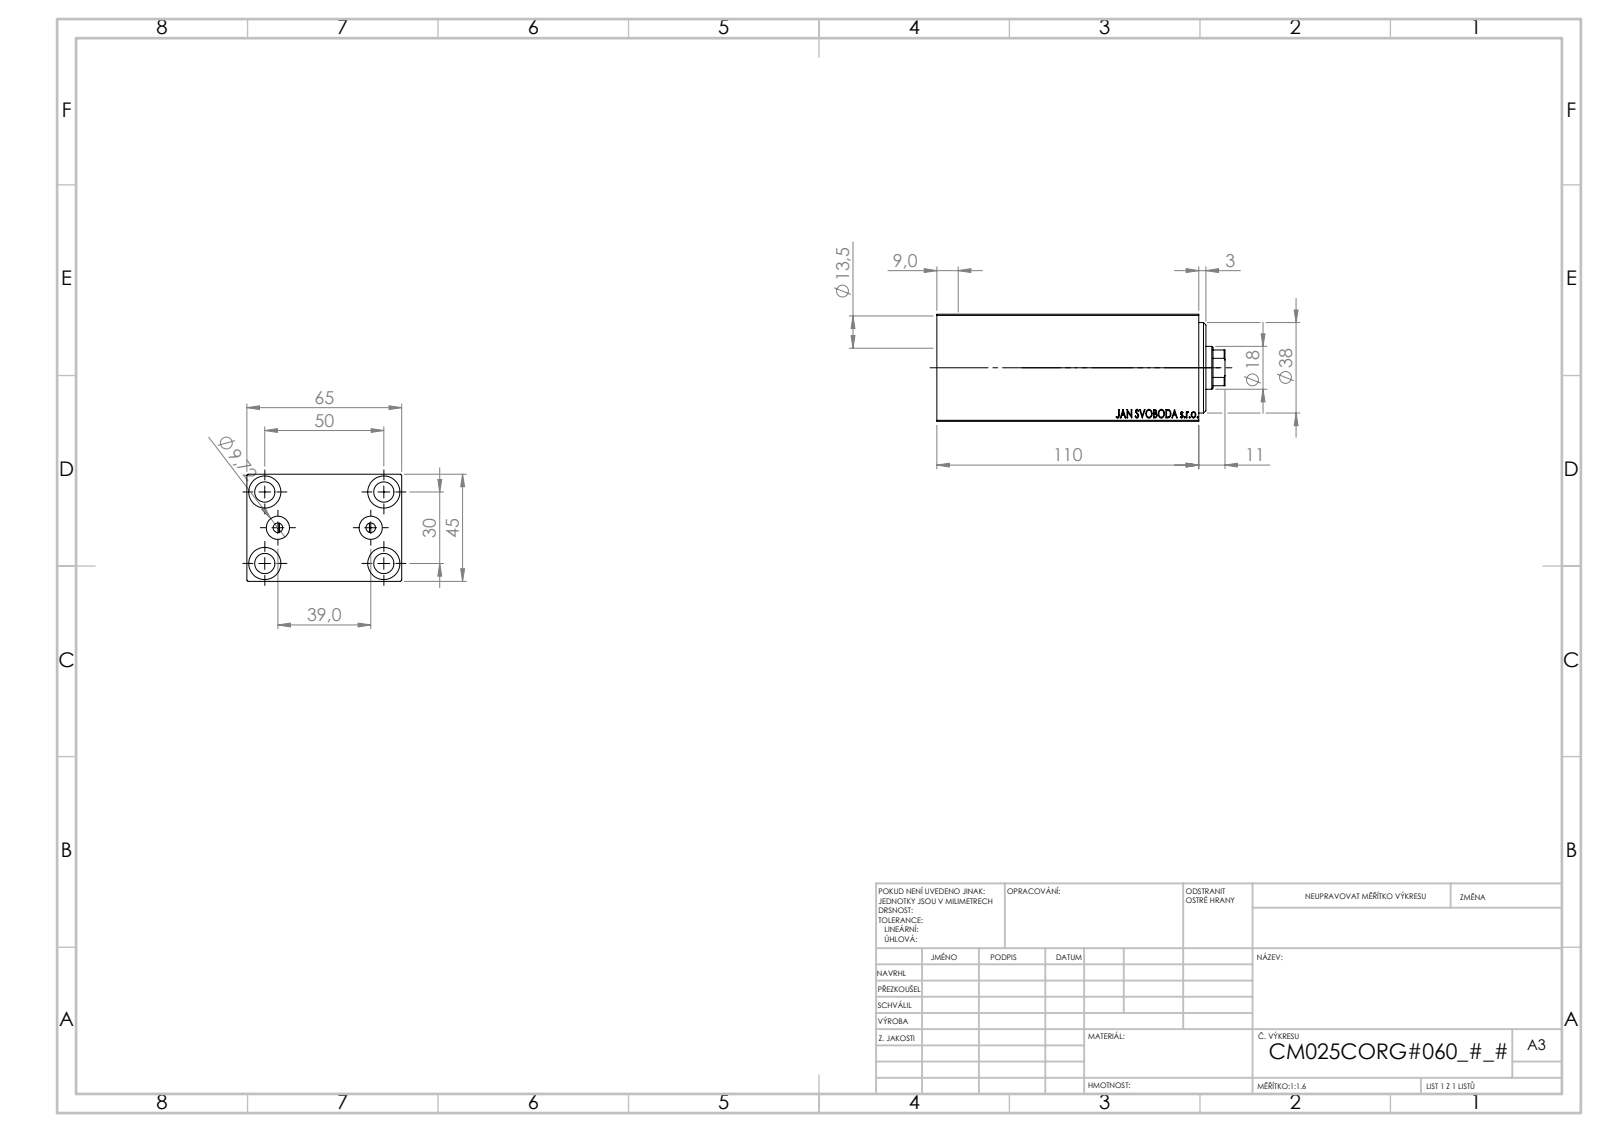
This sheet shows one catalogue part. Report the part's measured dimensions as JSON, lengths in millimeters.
{"part_name": "V450CM_VC_B; V450CM_C_Body; V450CM_C_VCP", "step_written_by": "SolidWorks 2019 (CONFIG_CONTROL_DESIGN)", "units": "millimeters", "bodies": {"solids": 3, "faces": 858, "planar": 408, "cylindrical": 56, "other": 394}, "overall_size": [121, 65, 45], "volume_mm3": 276431, "surface_area_mm2": 63244, "round_holes": [[8.5, 5], [13.5, 4], [4, 2], [9.72, 2], [18, 1], [21.5, 1], [25, 1], [27, 1], [38, 1]], "partial_cylinders_radius": [[8.5, 1]], "face_to_face_distances": [45, 65, 5, 105, 110, 25, 85, 80, 8, 9], "hole_center_spacings": [15.98, 29.15, 46.96, 19.5, 30, 50, 58.31, 39]}
